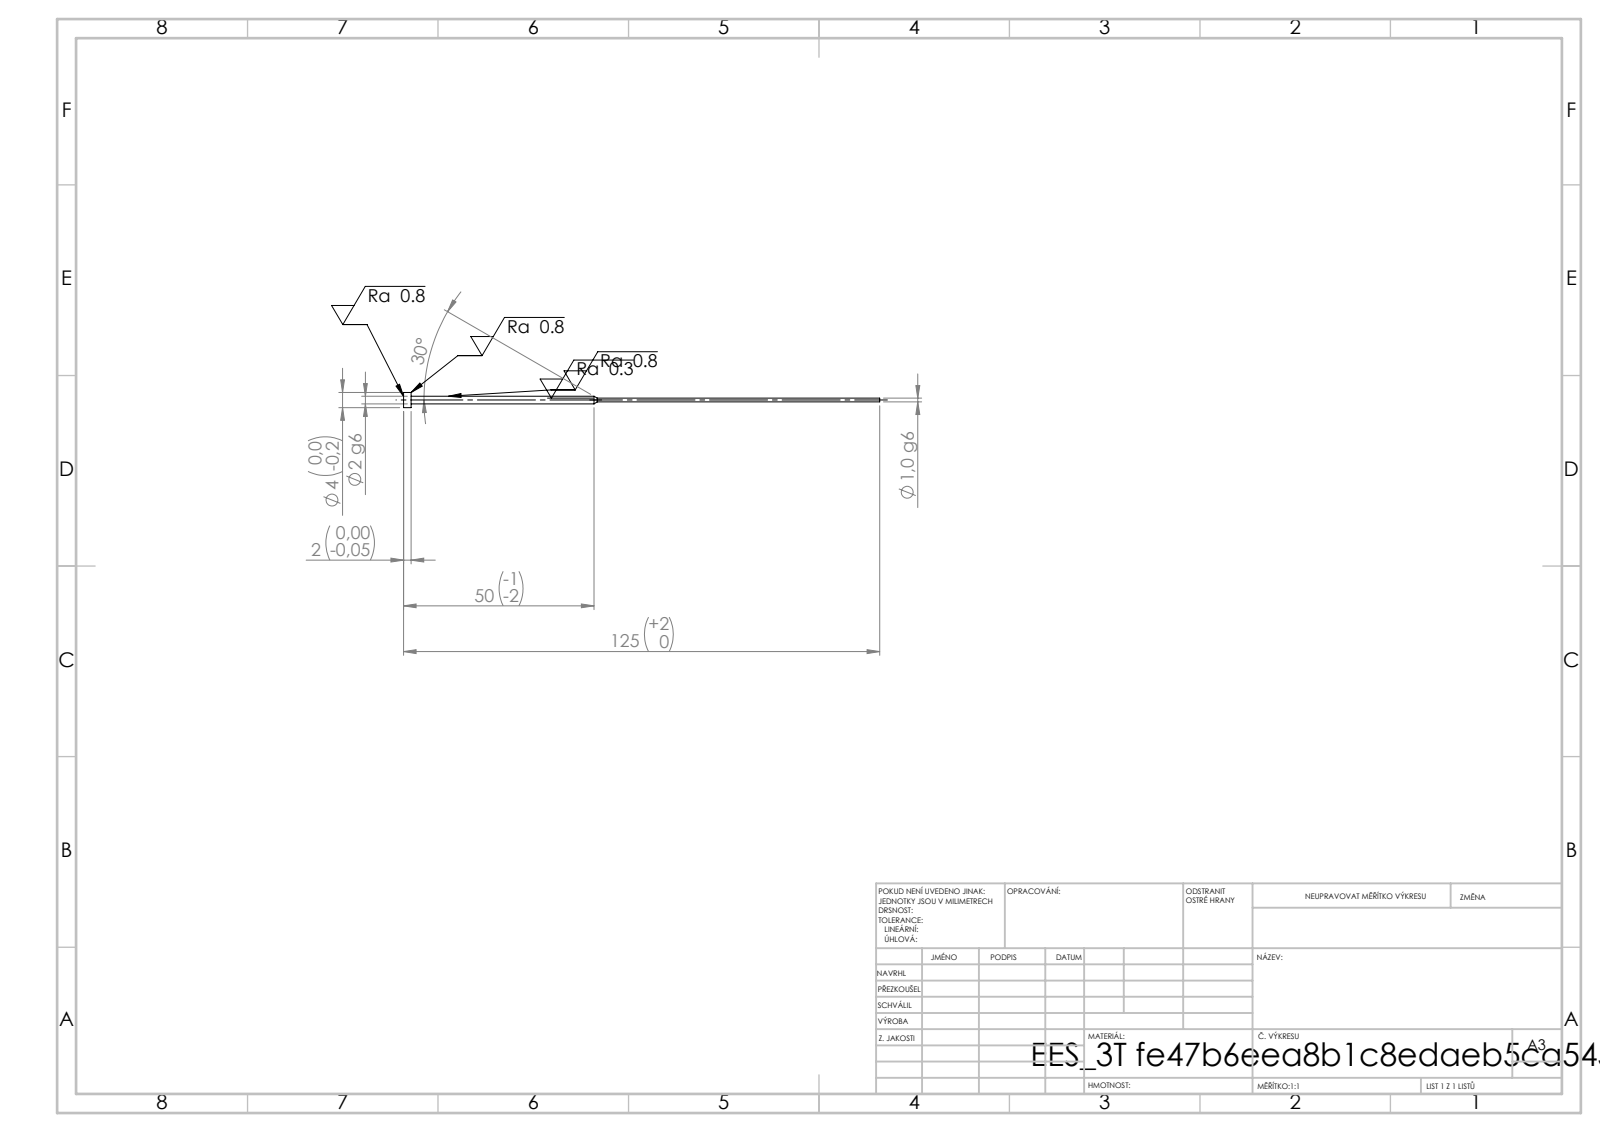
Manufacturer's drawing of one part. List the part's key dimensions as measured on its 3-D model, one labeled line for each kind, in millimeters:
STEP written by: SolidWorks 2019 (CONFIG_CONTROL_DESIGN)
Units: millimetres
Bodies: 1 solid, 11 faces (3 planar, 6 cylindrical, 2 other)
Overall size (bounding box): 125 × 4 × 4
Volume: 236 mm³ · Surface area: 587 mm²
Round bosses / shafts (diameter × count): ⌀4 ×1, ⌀2 ×1, ⌀1 ×1
Main face-to-face distances: 2, 123, 125
